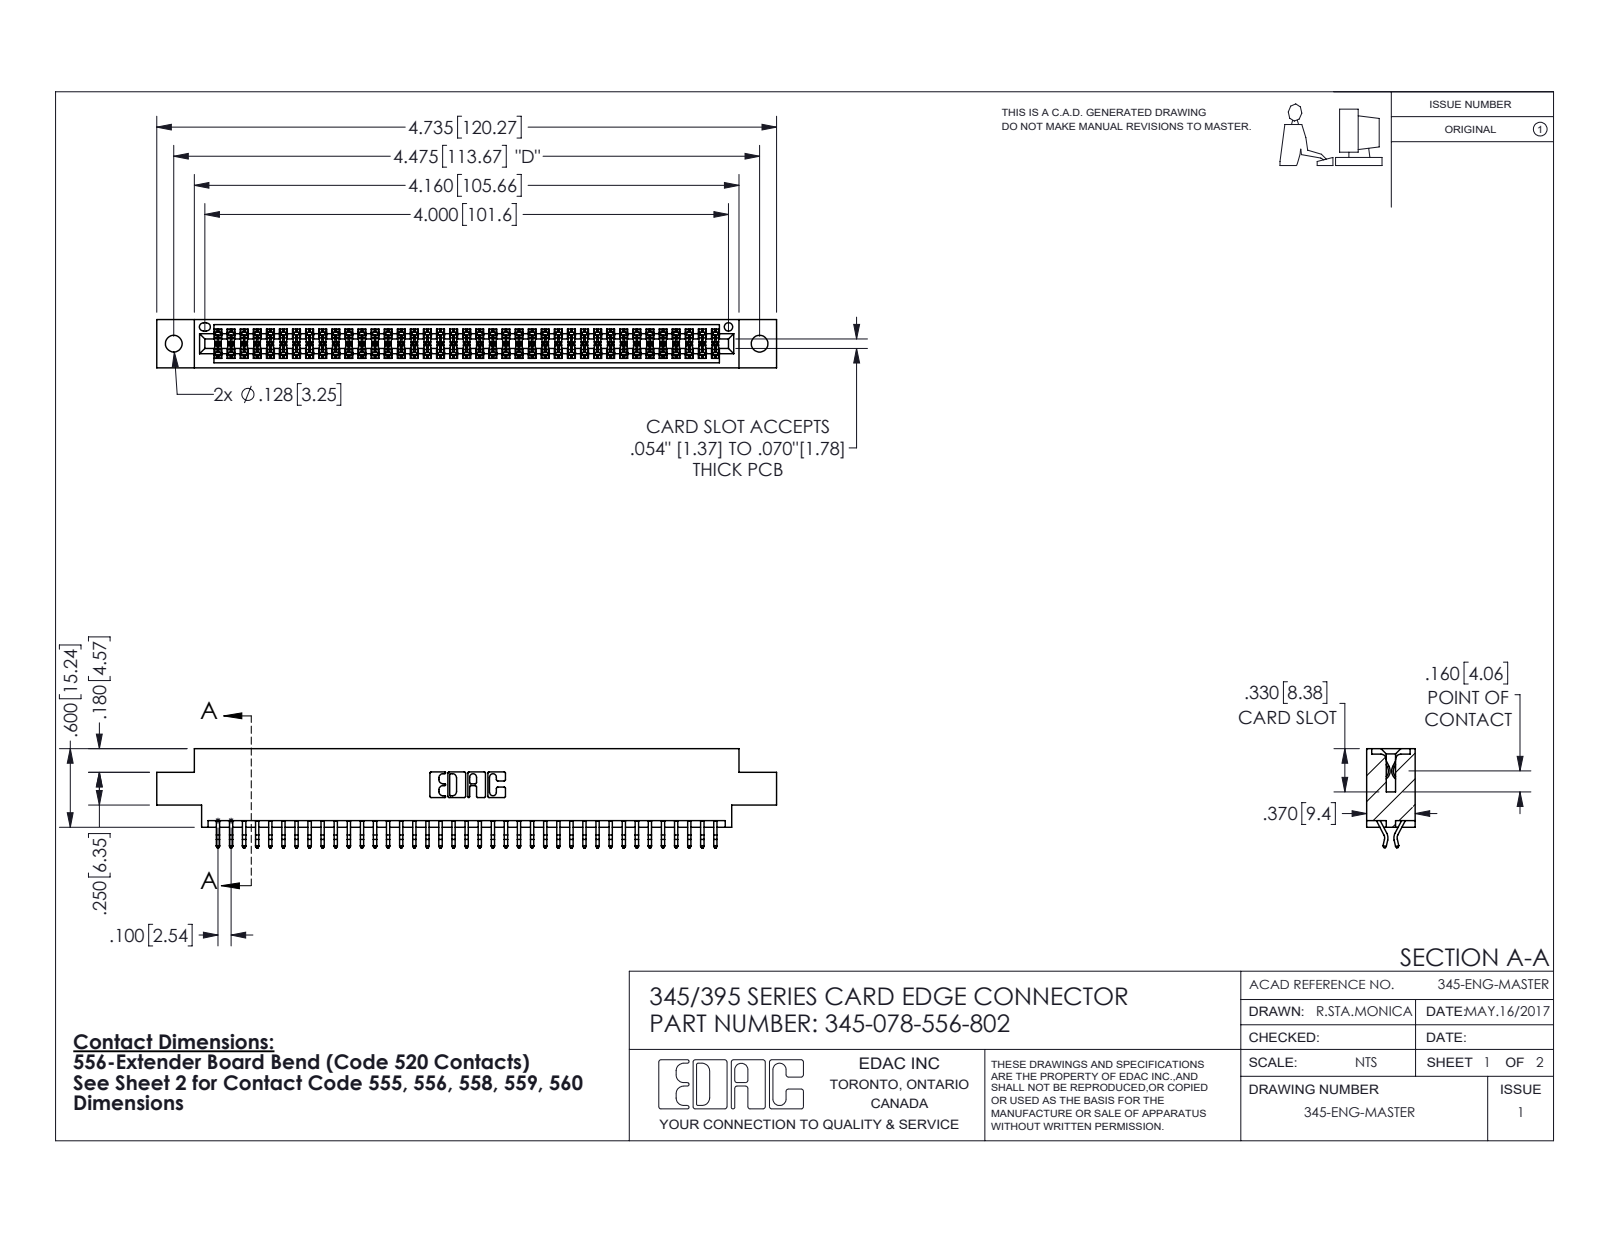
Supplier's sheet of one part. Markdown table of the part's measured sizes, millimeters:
| quantity | value |
| --- | --- |
| part name | 345-292-001_556 Tail; 345 Part_0.170 Offset - 0.128 Dia; 345-078-556-802 |
| STEP written by | SolidWorks 2016 (CONFIG_CONTROL_DESIGN) |
| units | millimeters |
| bodies | 79 solids, 4498 faces (2970 planar, 1528 cylindrical, 0 other) |
| overall size | 120.3 × 19.2 × 9.4 |
| volume | 11 500 mm³ |
| surface area | 16 750 mm² |
| round holes (diameter × count) | 3.3 × 2, 1.6 × 1 |
| partial cylindrical surfaces (radius × count) | 0.2 × 117, 0.3 × 22, 0.2 × 6, 0.8 × 6, 0.7 × 3, 0.3 × 2, 0.4 × 2, 0.5 × 2 |
| main face-to-face distances | 7.6, 1.8, 9.4, 5.1, 0.6, 2.5, 6.9, 5.7, 4.4, 3.8 |
| hole center spacings | 6.9, 107.7, 113.7 |
